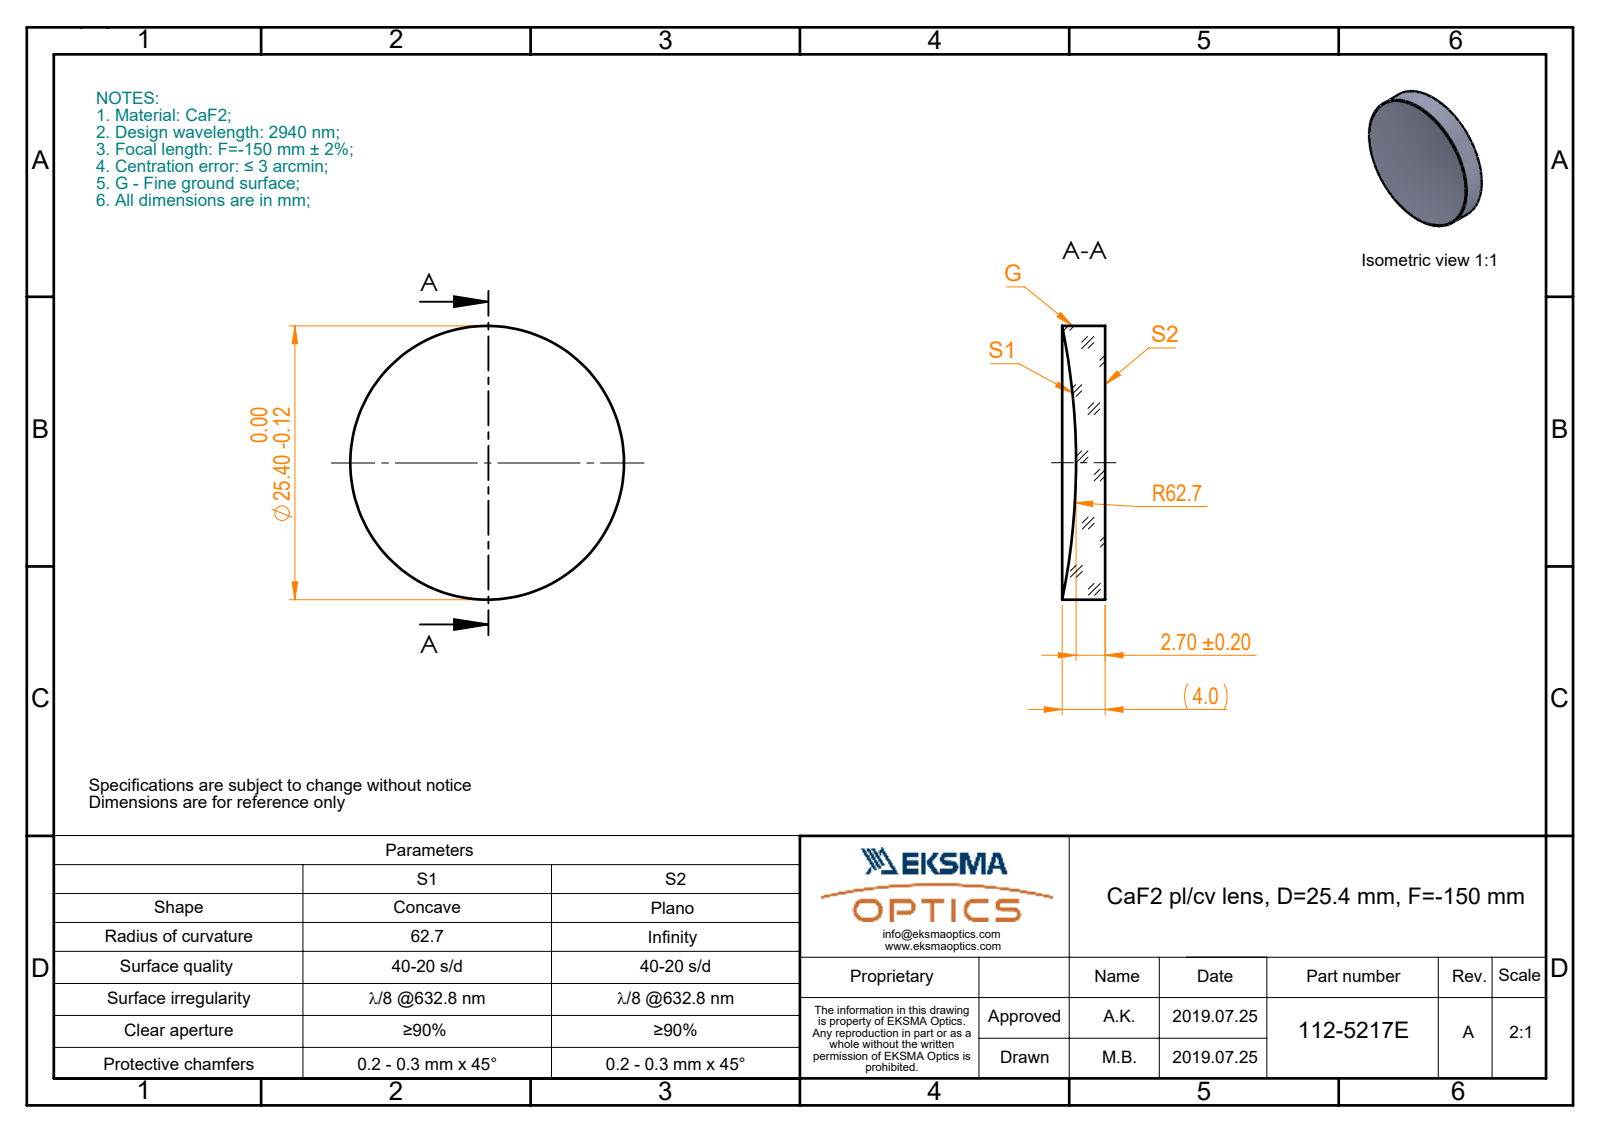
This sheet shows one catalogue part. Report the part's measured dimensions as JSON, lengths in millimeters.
{"part_name": "112-5217E CaF2 pl-cv 12.7 F-150", "step_written_by": "SolidWorks 2017 (CONFIG_CONTROL_DESIGN)", "units": "millimeters", "bodies": {"solids": 1, "faces": 5, "planar": 1, "cylindrical": 2, "other": 2}, "overall_size": [25.4, 25.4, 4], "volume_mm3": 1696, "surface_area_mm2": 1338, "round_bosses_or_shafts": [[25.4, 1]]}
